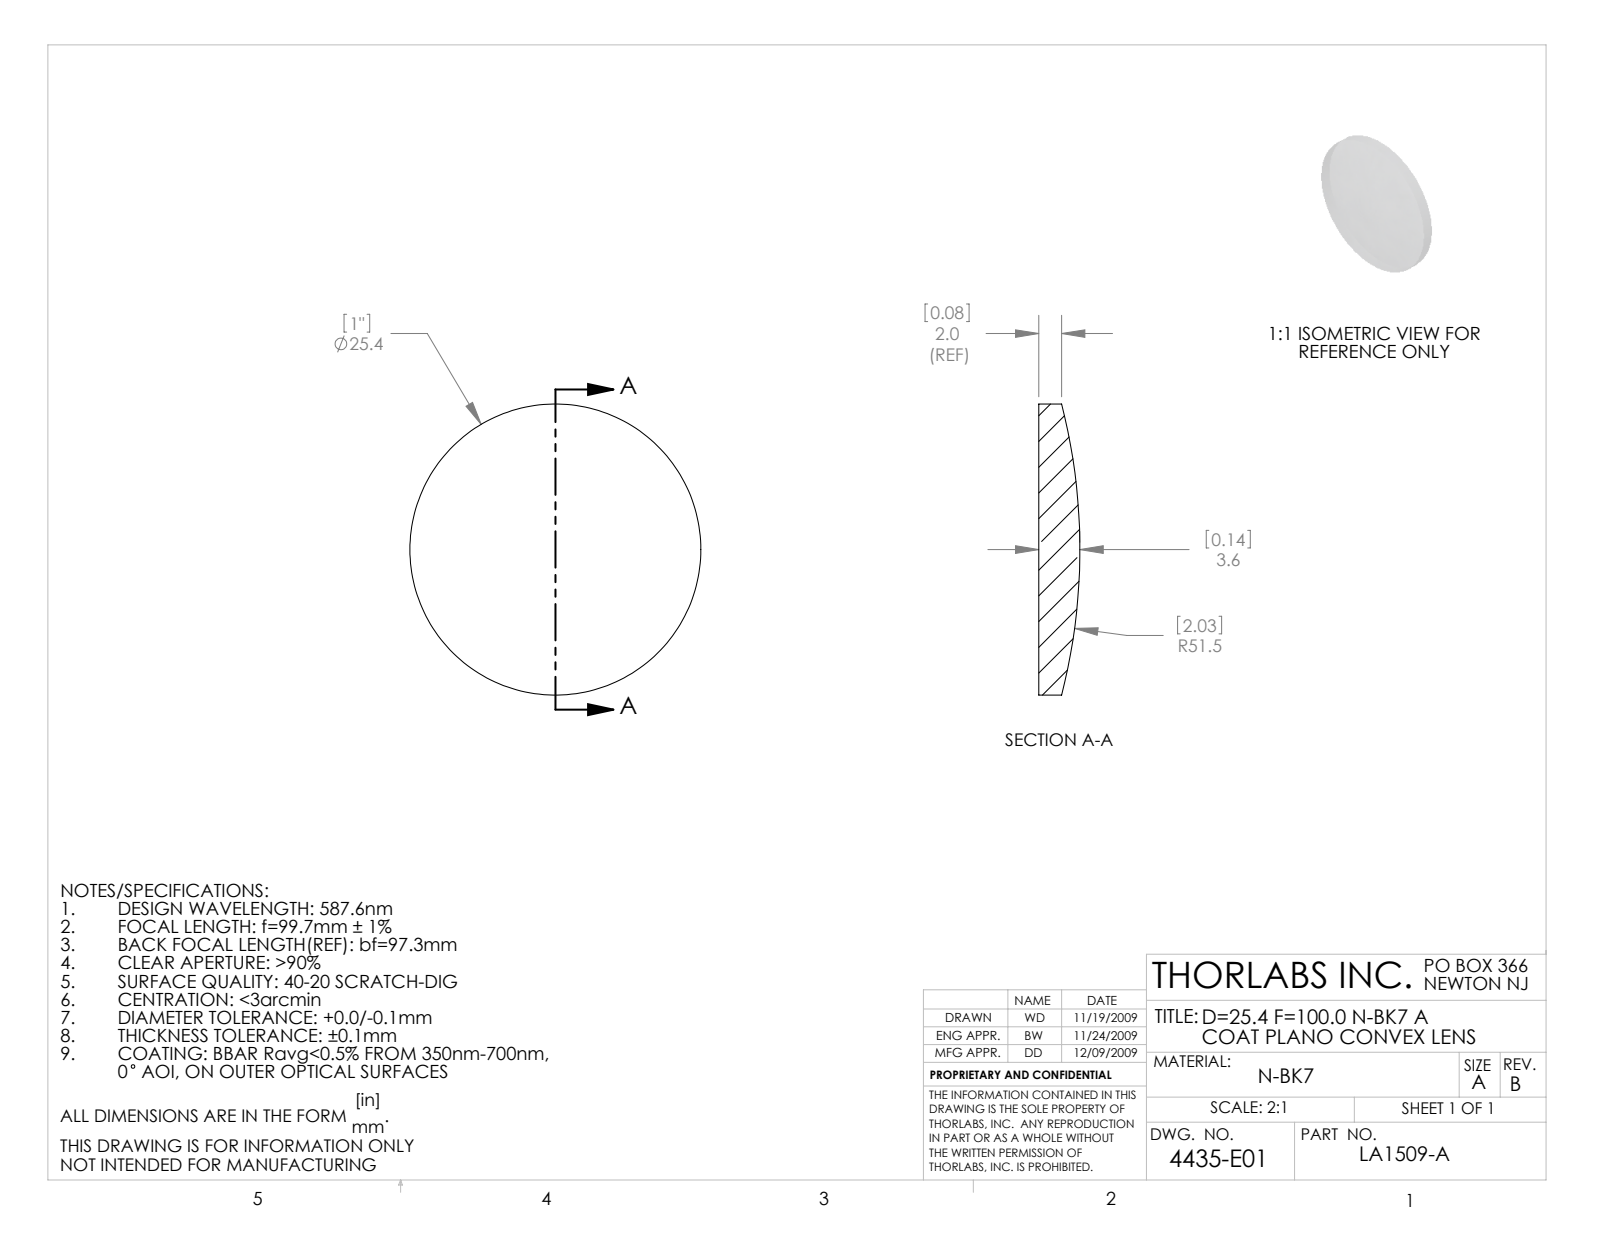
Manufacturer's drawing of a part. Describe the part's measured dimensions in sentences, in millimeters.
The part is named "4435-E0W". Its 3-D file was written by "SolidWorks 2009 (AUTOMOTIVE_DESIGN)". It is 1 solid with 5 faces: 1 planar, 2 cylindrical and 2 other. Overall it measures 25.4 by 25.4 by 3.59 millimeters. Its volume is 1 418 cubic millimeters and its surface area 1 181 square millimeters. Round bosses or shafts: 1 of diameter 25.4.
